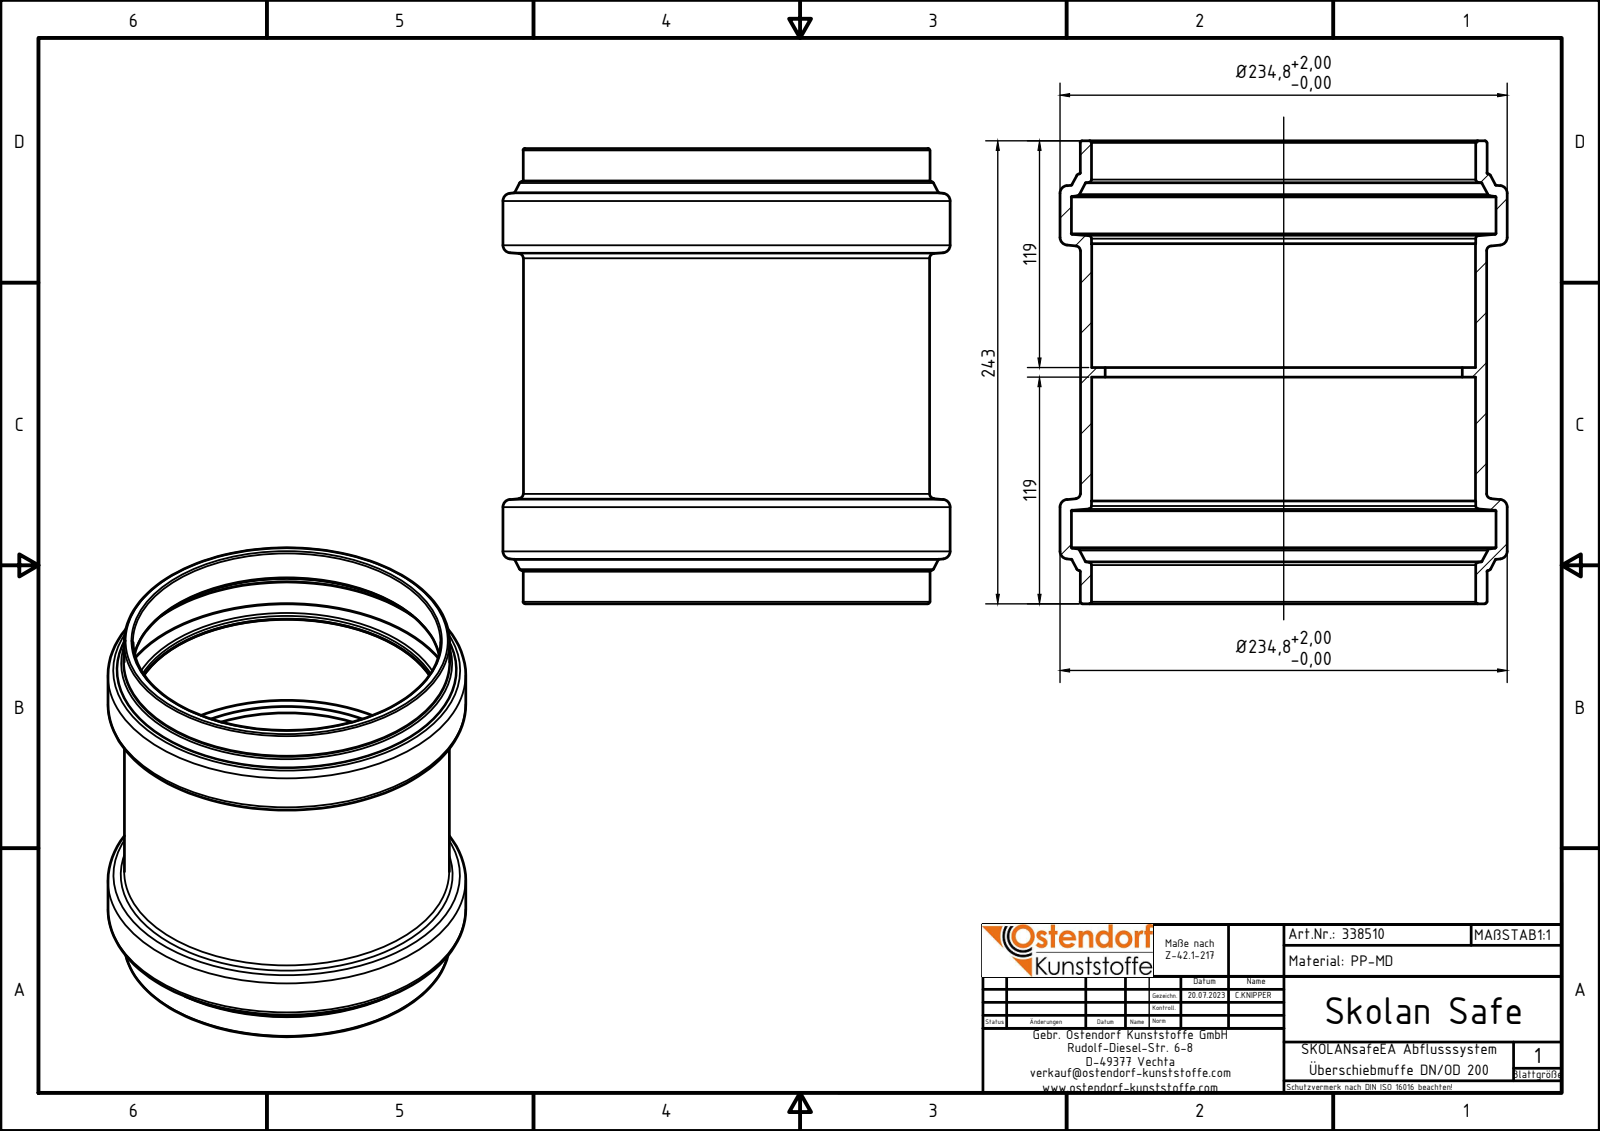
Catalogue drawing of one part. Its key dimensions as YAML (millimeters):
part_name: "338510z"
step_written_by: "Autodesk Inventor 2020 (AUTOMOTIVE_DESIGN)"
units: millimeters
bodies: {solids: 1, faces: 62, planar: 6, cylindrical: 14, other: 42}
overall_size: [243, 234.8, 234.8]
volume: 1106000
surface_area: 378918
round_holes:
  - {diameter: 187.5, count: 1}
  - {diameter: 201.5, count: 1}
  - {diameter: 201.8, count: 1}
  - {diameter: 223, count: 1}
round_bosses_or_shafts:
  - {diameter: 234.8, count: 1}
  - {diameter: 213.6, count: 1}
  - {diameter: 213.3, count: 1}
face_to_face_distances: [119, 124, 5, 243, 53.93, 189.07, 65.07, 70.07, 135.14]
